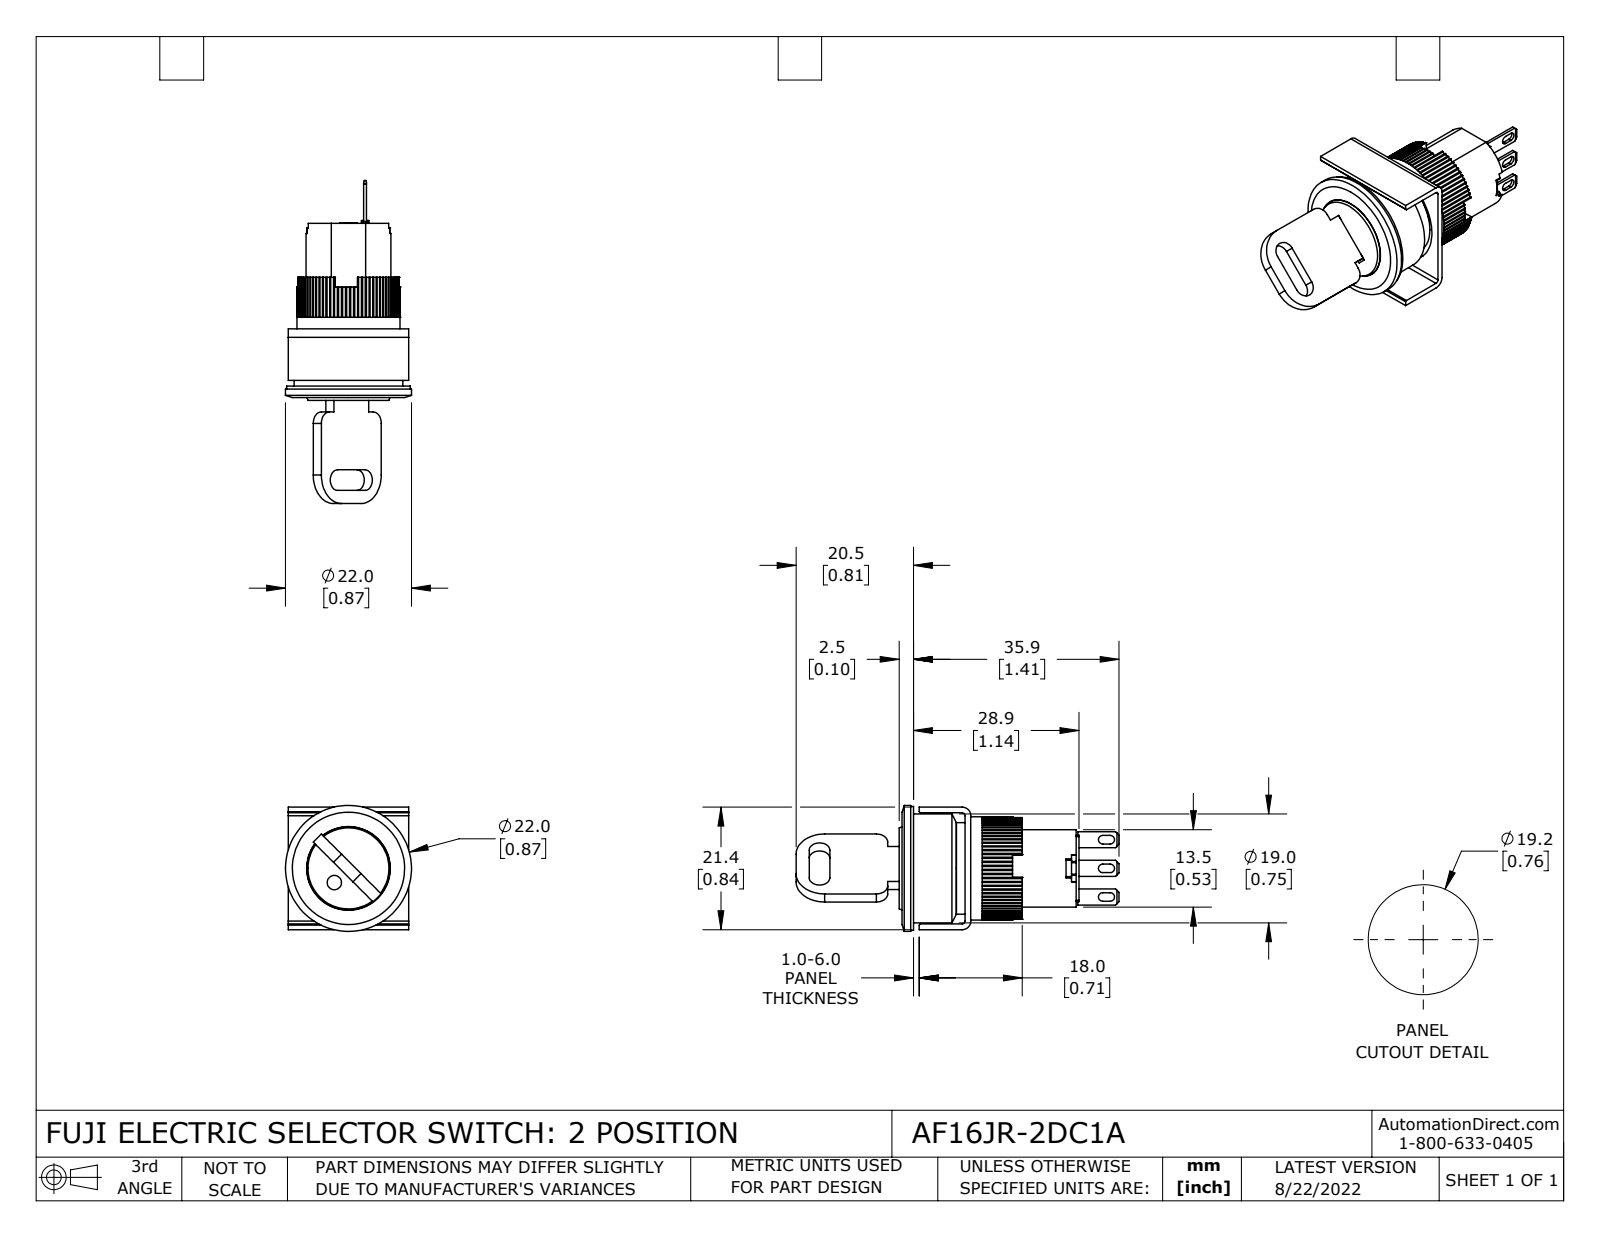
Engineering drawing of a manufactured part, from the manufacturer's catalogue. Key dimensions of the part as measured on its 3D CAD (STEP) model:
Part name (STEP PRODUCT): AF16JR-2DC1A
STEP written by: SolidWorks 2021 (CONFIG_CONTROL_DESIGN)
Units: inches
Bodies: 10 solids, 639 faces (456 planar, 177 cylindrical, 6 other)
Overall size (bounding box): 2.22 × 0.866 × 0.866
Volume: 0.493 in³ · Surface area: 11.01 in²
Round holes (diameter × count): ⌀0.039 ×1, ⌀0.098 ×1, ⌀0.575 ×1, ⌀0.709 ×1, ⌀0.748 ×1
Round bosses / shafts (diameter × count): ⌀0.866 ×1, ⌀0.85 ×1, ⌀0.63 ×1, ⌀0.583 ×1, ⌀0.571 ×1
Partial cylindrical surfaces — rounded edges, fillets, slot ends (radius × count): R0.01 ×80, R0.008 ×12, R0.03 ×6, R0.02 ×2, R0.059 ×2, R0.071 ×2, R0.079 ×2, R0.197 ×2
Main face-to-face distances: 0.079, 0.039, 0.02, 0.374, 0.177, 0.394, 0.803, 0.098, 0.059, 0.764
Hole centre spacings: 0.137
